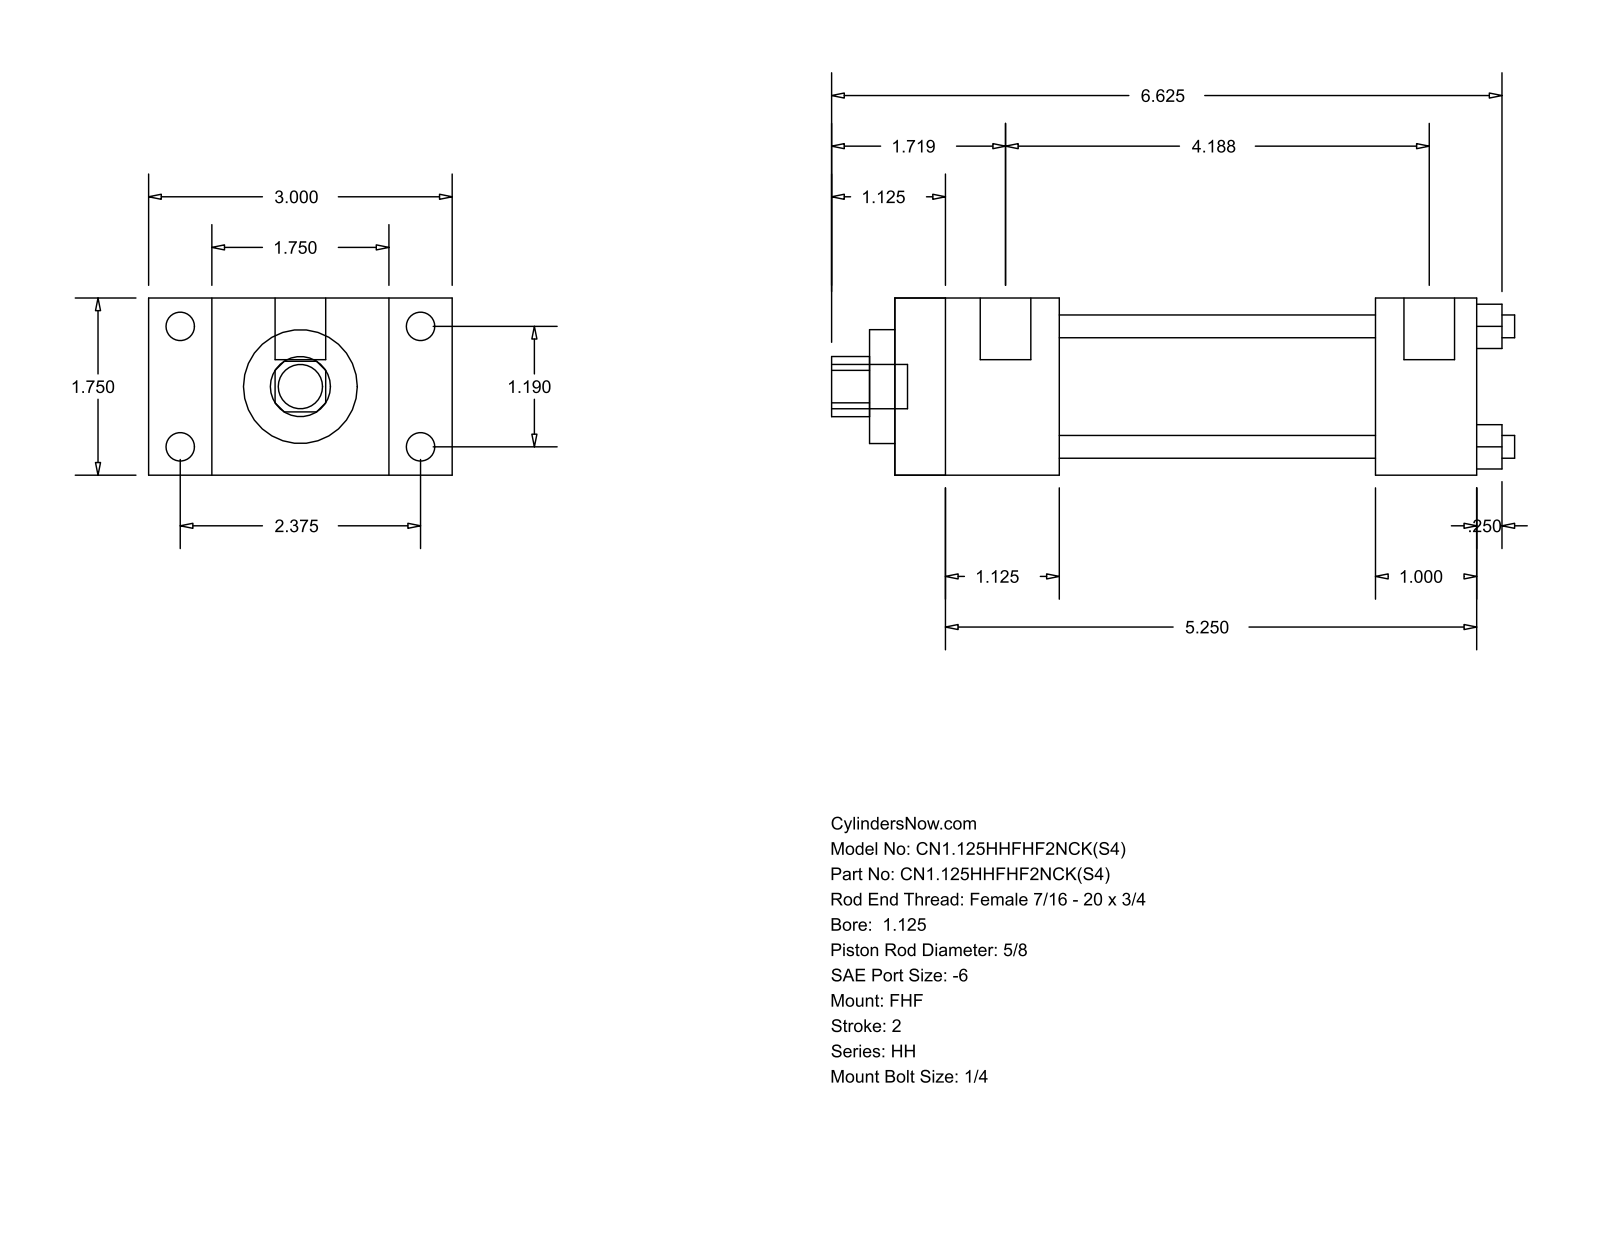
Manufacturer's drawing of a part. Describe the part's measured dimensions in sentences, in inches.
The part is named "HH_FHF__0112_0.625". Its 3-D file was written by "GSSL Pune (CONFIG_CONTROL_DESIGN)". It is 0 solids with 88 faces: 60 planar, 28 cylindrical and 0 other. Overall it measures 6.75 by 3 by 1.75 inches. Round holes: 4 of diameter 0.225, 1 of diameter 0.625, 1 of diameter 1.125, 1 of diameter 1.375. Round bosses or shafts: 4 of diameter 0.281, 4 of diameter 0.219, 2 of diameter 0.5, 1 of diameter 0.437. Partial cylindrical surfaces (rounded edges, fillets, slot ends): 1 of radius 0.297. The main face-to-face distances are 1.75, 0.625, 2.375, 1.625, 3, 5.75, 4.125, 4.75, 3.125, 1. The hole center spacings are 0.841, 1.19, 1.683.
